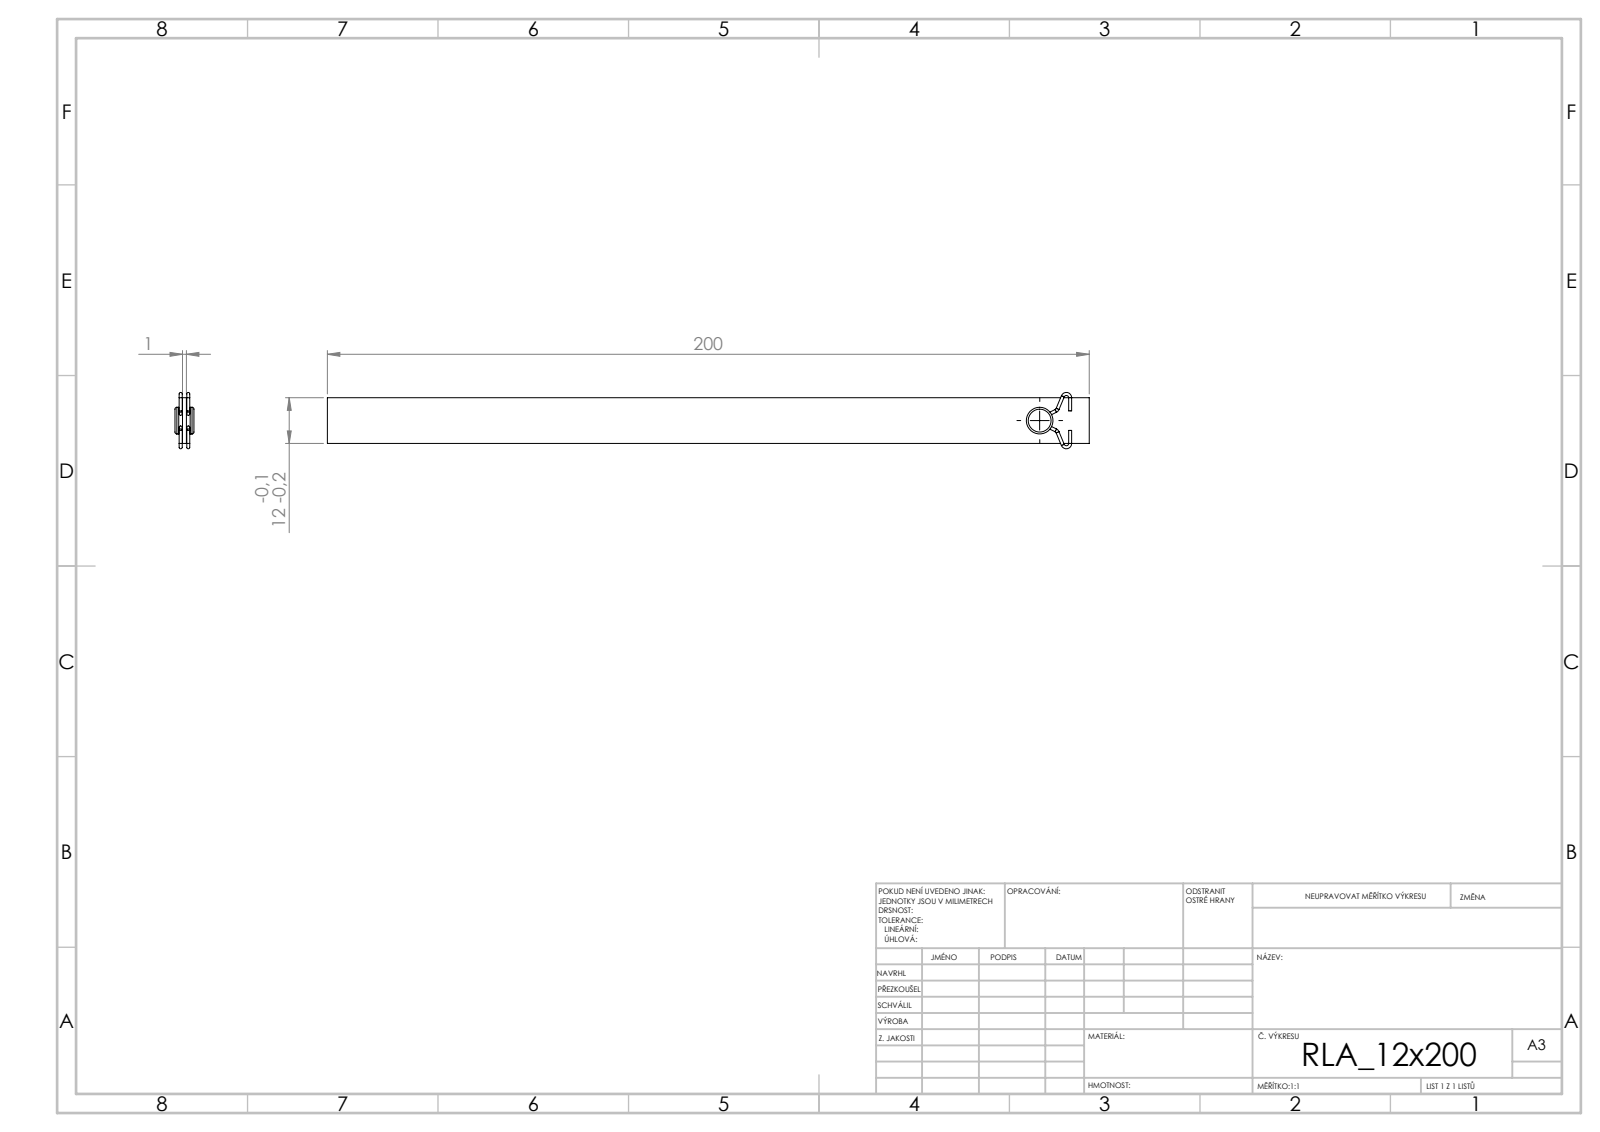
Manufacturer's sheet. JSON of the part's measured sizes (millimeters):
{"step_written_by": "SolidWorks 2019 (CONFIG_CONTROL_DESIGN)", "units": "millimeters", "bodies": {"solids": 3, "faces": 82, "planar": 14, "cylindrical": 40, "other": 28}, "overall_size": [200, 14.8, 5], "volume_mm3": 2538, "surface_area_mm2": 5580, "round_bosses_or_shafts": [[0.8, 14], [7, 1], [4, 1]], "face_to_face_distances": [1, 12, 2, 3, 4, 5, 200, 3.45, 8.55, 5.1]}
